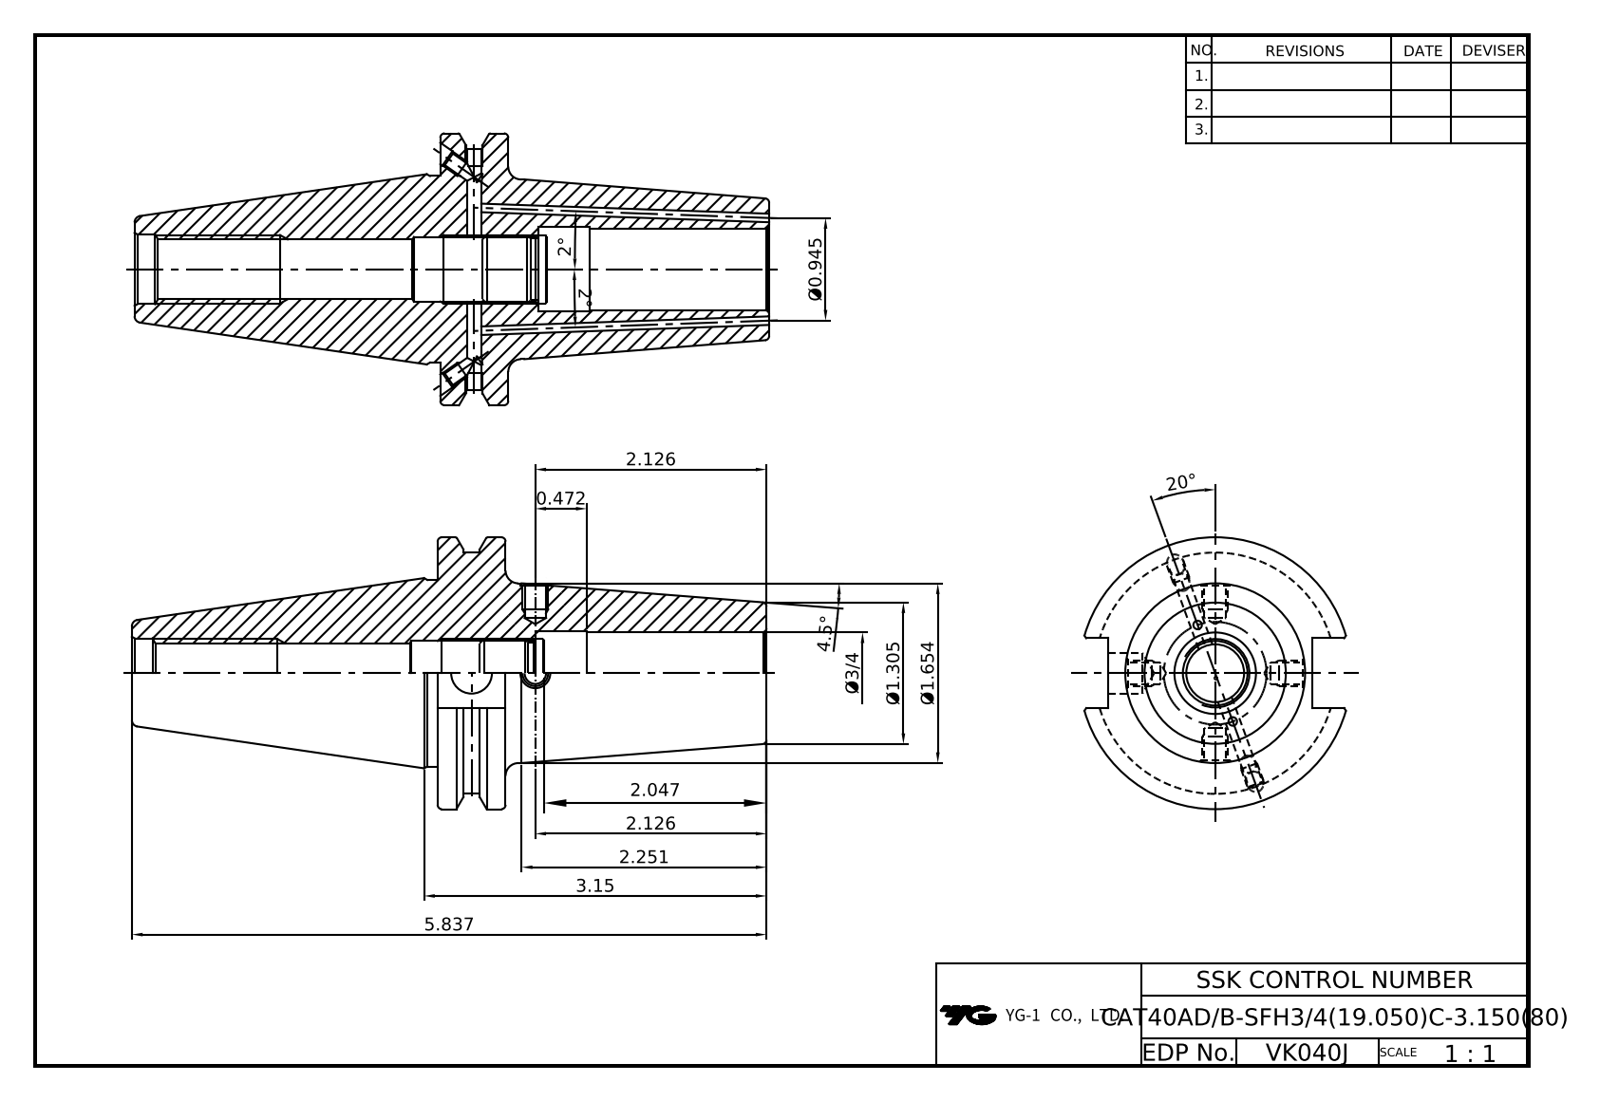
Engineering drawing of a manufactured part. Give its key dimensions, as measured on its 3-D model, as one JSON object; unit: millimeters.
{"part_name": "LO-CAT40ADB-SFH19.05C-80", "step_written_by": "Autodesk Inventor 2024 (AUTOMOTIVE_DESIGN)", "units": "millimeters", "bodies": {"solids": 1, "faces": 92, "planar": 39, "cylindrical": 31, "other": 22}, "overall_size": [148.25, 63.5, 61.09], "volume_mm3": 151433, "surface_area_mm2": 31651, "round_holes": [[3.24, 4], [2.5, 2], [4, 2], [4.2, 2], [9.53, 1], [13, 1], [13.39, 1], [14.92, 1], [16.3, 1], [19.05, 1], [19.65, 1]], "round_bosses_or_shafts": [[63.5, 1], [43.6, 1], [42, 1]], "partial_cylinders_radius": [[28.15, 1]], "face_to_face_distances": [15.88, 76.83, 60.95, 47.6, 16.38, 71.42, 87.3, 148.25, 94.25, 22.83]}
